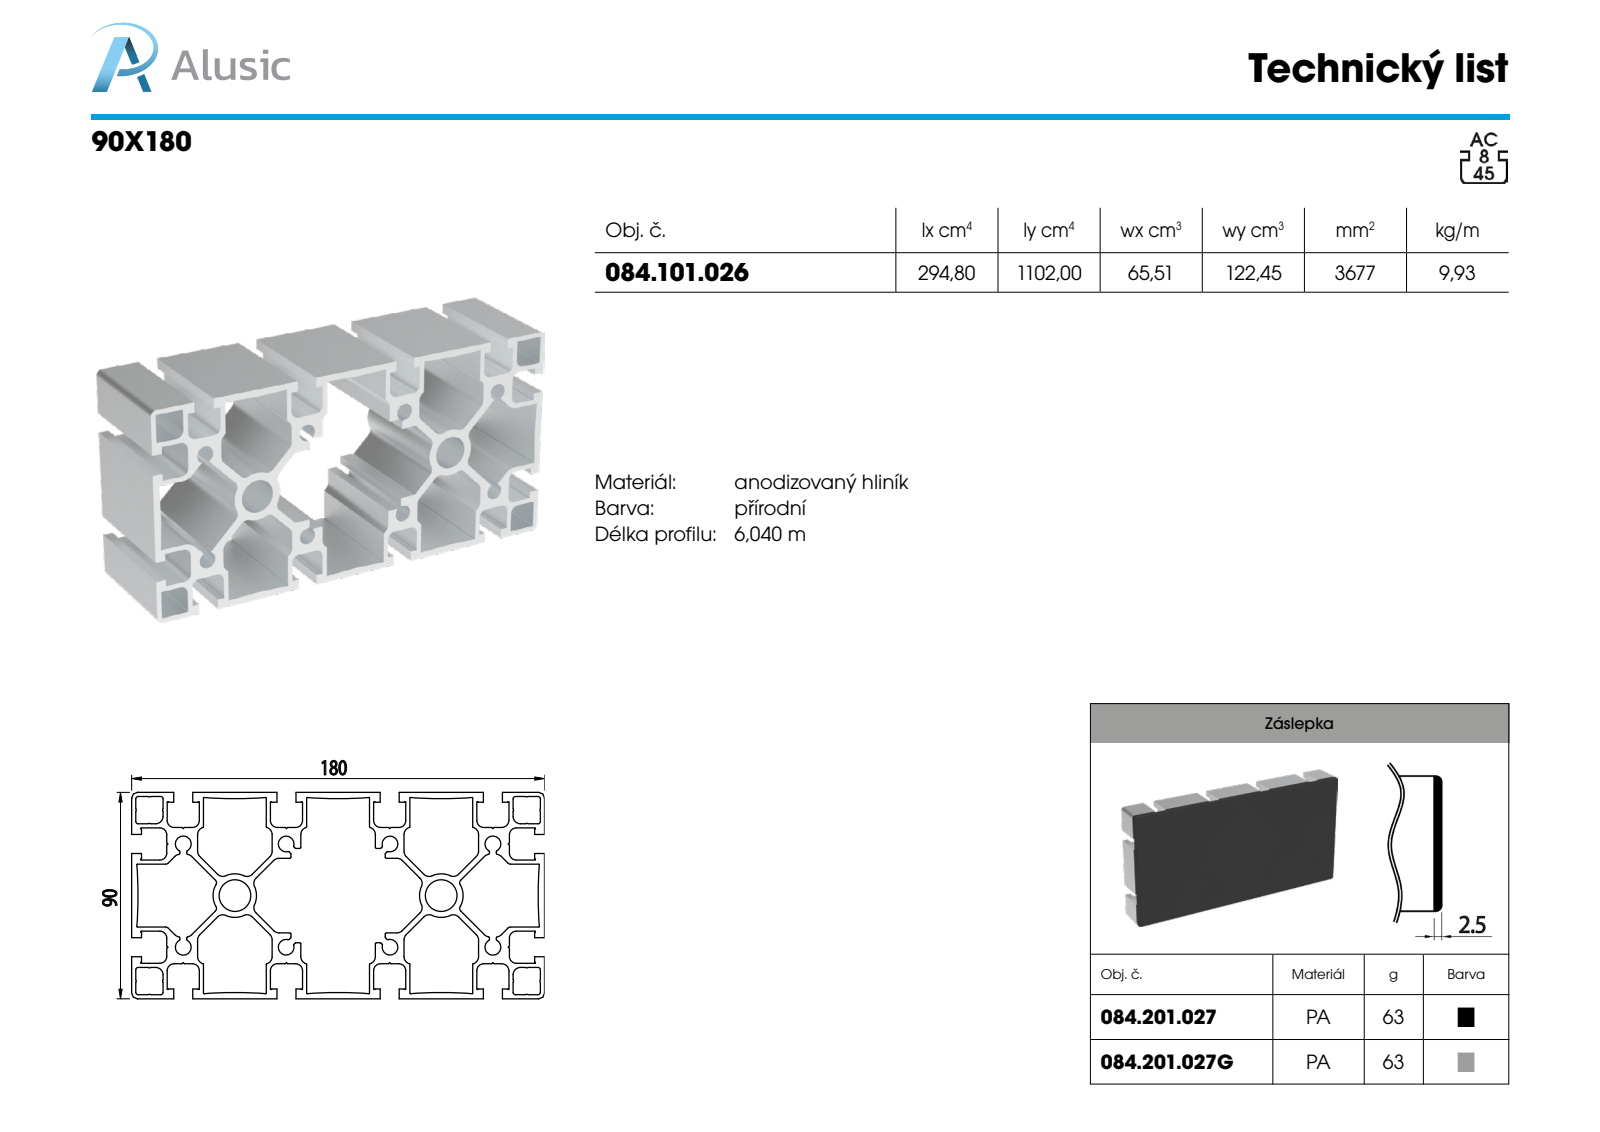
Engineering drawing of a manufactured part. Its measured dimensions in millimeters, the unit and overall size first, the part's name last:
Units: millimetres
Overall size (bounding box): 180 × 100 × 90
Round holes (diameter × count): ⌀6.9 ×8, ⌀13.8 ×2
Partial cylindrical surfaces — rounded edges, fillets, slot ends (radius × count): R3.2 ×40, R3 ×24, R0.5 ×12, R2.5 ×4, R6 ×4, R10.1 ×2
Main face-to-face distances: 45, 2, 90, 16, 29, 29.5, 43, 58.5, 74.5, 47
Hole centre spacings: 45, 31.82, 63.64, 90, 71.15, 100.62, 114.73, 135
Volume: 369 431 mm³ · Surface area: 247 165 mm²
Bodies: 1 solid, 334 faces (214 planar, 120 cylindrical, 0 other)
Part name (STEP PRODUCT): 084.101.026
STEP written by: SolidWorks 2018 (AUTOMOTIVE_DESIGN)
